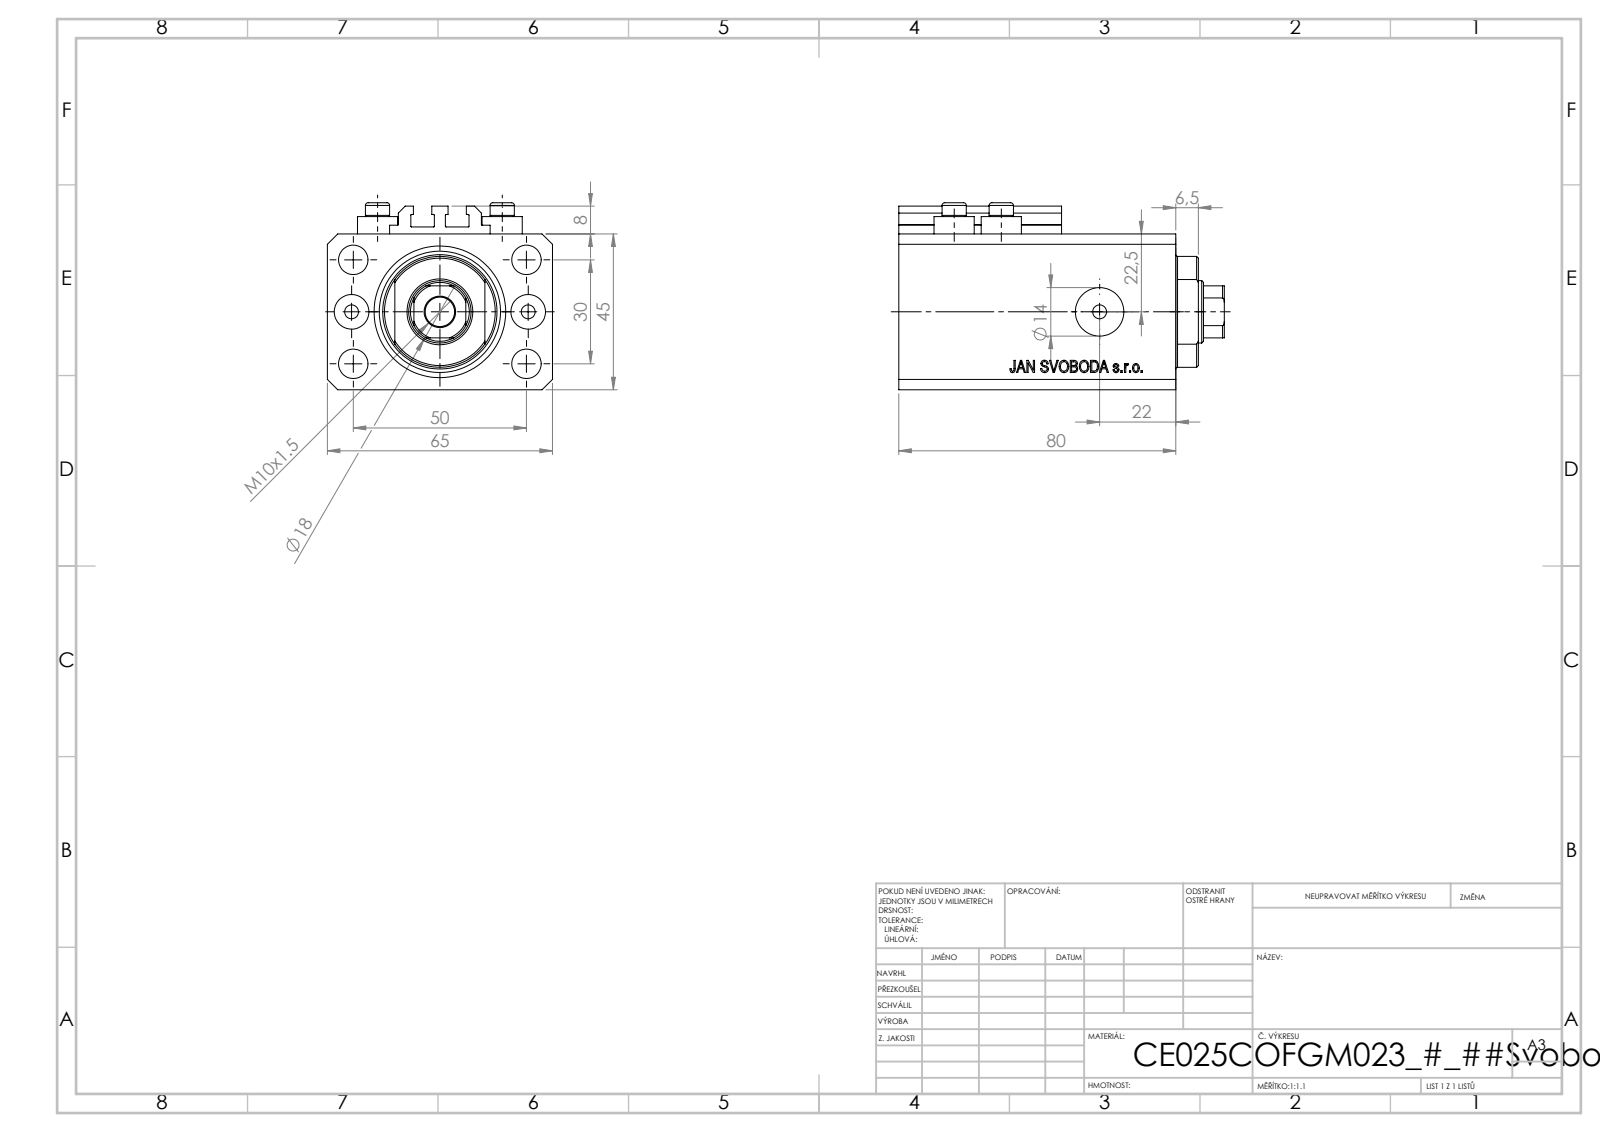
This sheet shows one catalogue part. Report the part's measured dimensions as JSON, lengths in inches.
{"part_name": "ALLEN BOLT V250CE; V250CE_VC_C; V250CE_C_Body; V250CE_C_VCP", "step_written_by": "SolidWorks 2019 (CONFIG_CONTROL_DESIGN)", "units": "inches", "bodies": {"solids": 8, "faces": 1034, "planar": 504, "cylindrical": 86, "other": 444}, "overall_size": [3.701, 2.559, 2.126], "volume_in3": 13.4, "surface_area_in2": 91.35, "round_holes": [[0.157, 8], [0.335, 5], [0.394, 2], [0.551, 2], [0.709, 1], [0.984, 1], [1.496, 1]], "round_bosses_or_shafts": [[0.457, 4], [0.276, 4]], "partial_cylinders_radius": [[0.008, 10], [0.335, 1], [0.63, 1]], "face_to_face_distances": [1.772, 2.559, 0.551, 2.598, 3.15, 1.85, 0.272, 2.327, 2.878, 0.118], "hole_center_spacings": [0.591, 1.148, 2.074, 1.417, 0.535, 1.004, 1.181, 1.515]}
